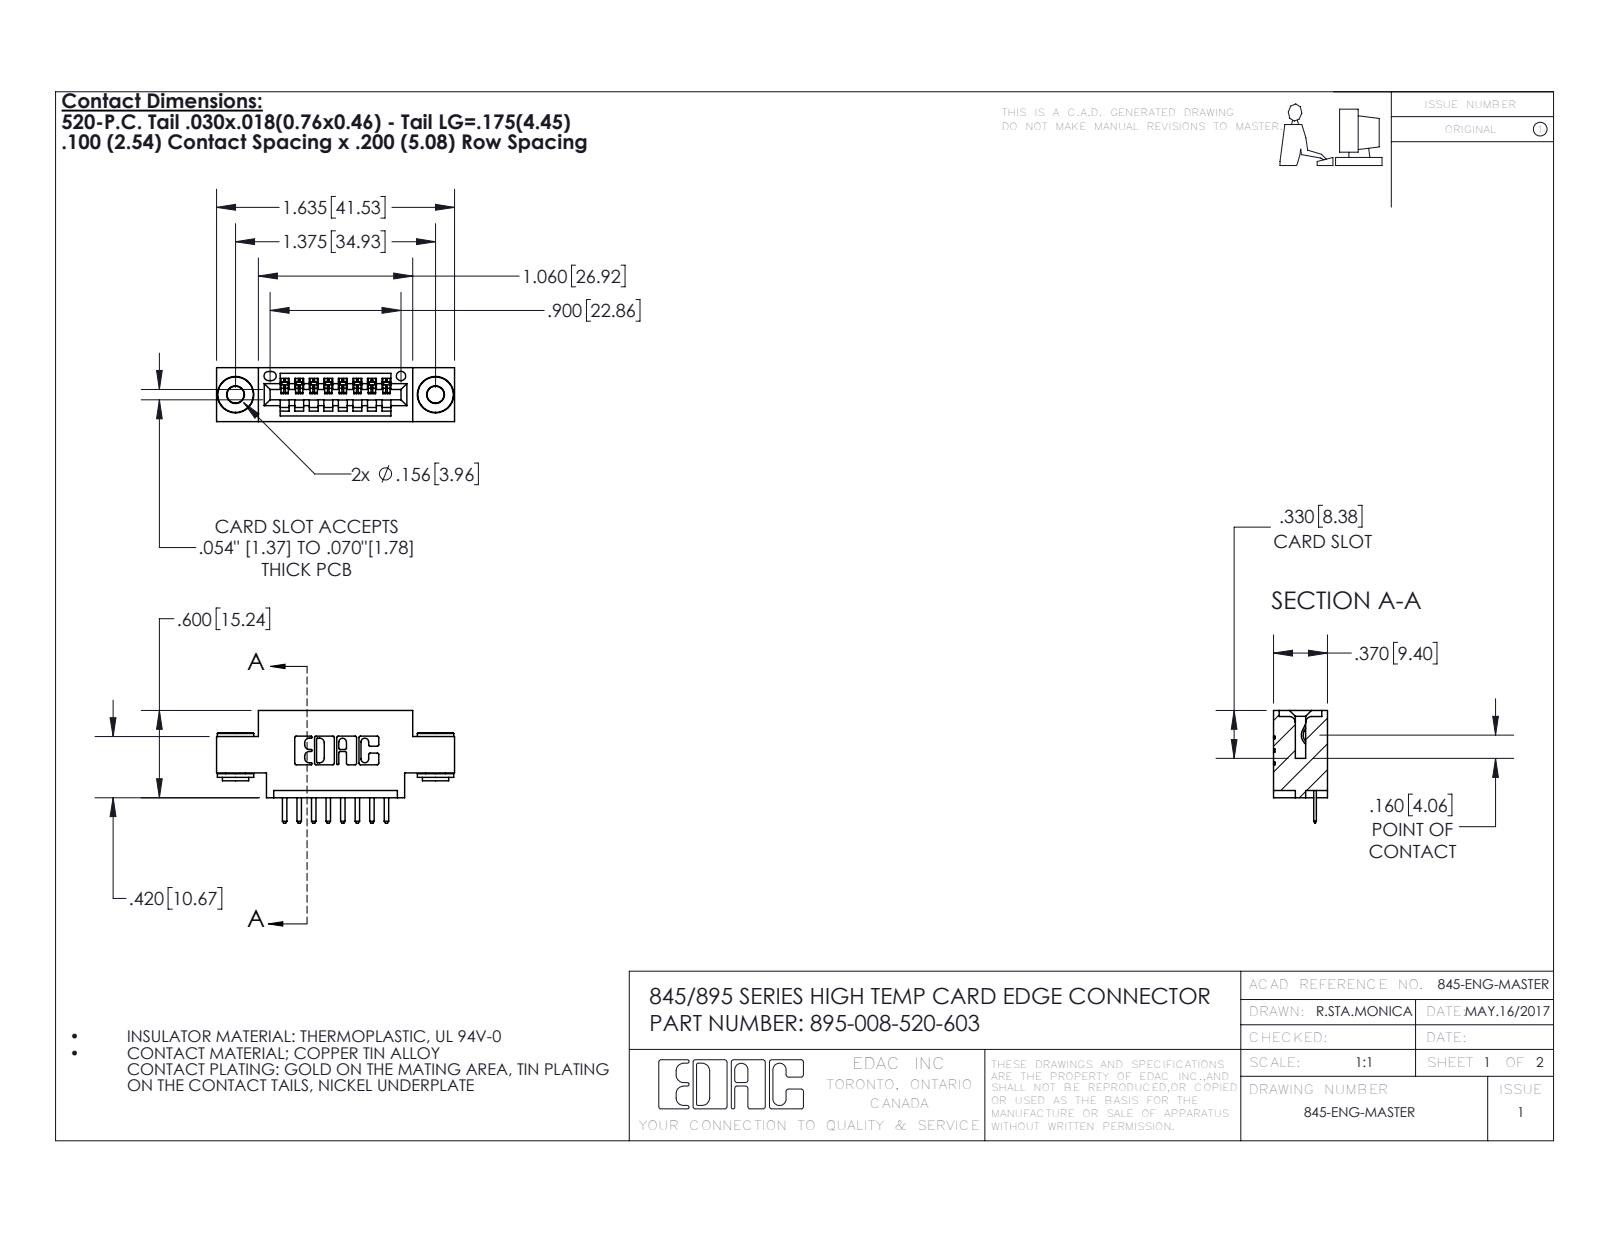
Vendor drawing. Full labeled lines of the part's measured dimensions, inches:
Part name (STEP PRODUCT): 395-008-520-603; 345-292-001_345-293-120; 345-250-002_345-250-002-102; 345 Part_0.170 Offset - 0.156 Dia-TH
STEP written by: SolidWorks 2016 (CONFIG_CONTROL_DESIGN)
Units: inches
Bodies: 11 solids, 664 faces (430 planar, 226 cylindrical, 8 other)
Overall size (bounding box): 1.635 × 0.775 × 0.37
Volume: 0.217 in³ · Surface area: 7.006 in²
Round holes (diameter × count): ⌀0.116 ×2, ⌀0.156 ×2, ⌀0.064 ×1
Round bosses / shafts (diameter × count): ⌀0.25 ×2, ⌀0.18 ×2, ⌀0.136 ×2
Partial cylindrical surfaces — rounded edges, fillets, slot ends (radius × count): R0.01 ×22, R0.01 ×18, R0.006 ×16, R0.007 ×6, R0.031 ×6, R0.026 ×3, R0.031 ×2, R0.04 ×2
Main face-to-face distances: 0.37, 0.2, 0.072, 0.298, 0.1, 0.098, 0.272, 0.025, 0.06, 0.25
Hole centre spacings: 0.27, 1.144, 1.375
